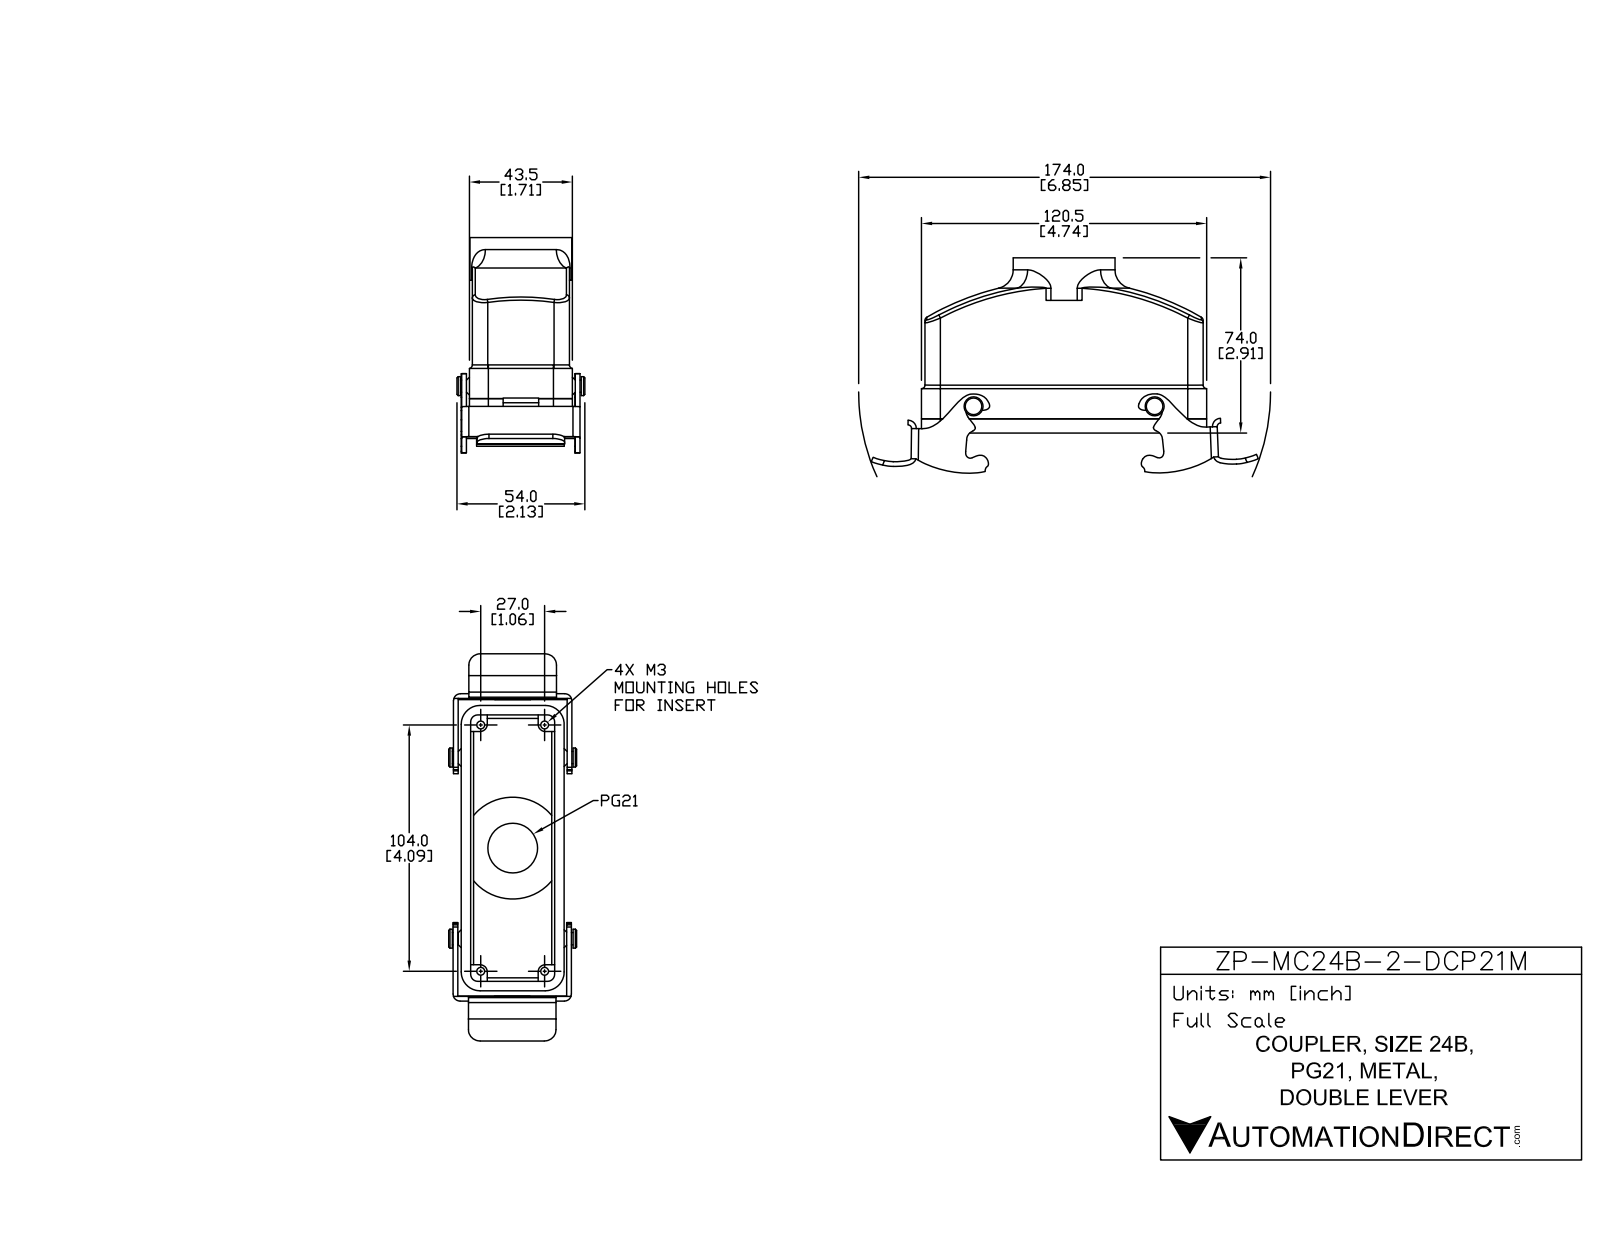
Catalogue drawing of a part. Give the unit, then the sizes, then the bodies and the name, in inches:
Units: inches
Overall size (bounding box): 6.022 × 3.455 × 2.126
Round holes (diameter × count): ⌀0.13 ×4, ⌀0.827 ×1, ⌀1.063 ×1
Round bosses / shafts (diameter × count): ⌀0.315 ×2, ⌀0.204 ×2, ⌀1.693 ×1
Partial cylindrical surfaces — rounded edges, fillets, slot ends (radius × count): R0.039 ×12, R0.02 ×10, R0.118 ×10, R0.315 ×8, R0.079 ×6, R0.157 ×6, R0.03 ×4, R0.059 ×4
Main face-to-face distances: 0.157, 0.049, 1.506, 1.457, 0.207, 1.555, 1.713, 1.663, 1.614, 0.039
Hole centre spacings: 2.115, 1.063, 4.094, 4.23
Volume: 6.245 in³ · Surface area: 91.36 in²
Bodies: 8 solids, 319 faces (130 planar, 153 cylindrical, 36 other)
Part name (STEP PRODUCT): ZP-MC24B-2-DCP21M
STEP written by: SolidWorks 2011 (AUTOMOTIVE_DESIGN)
